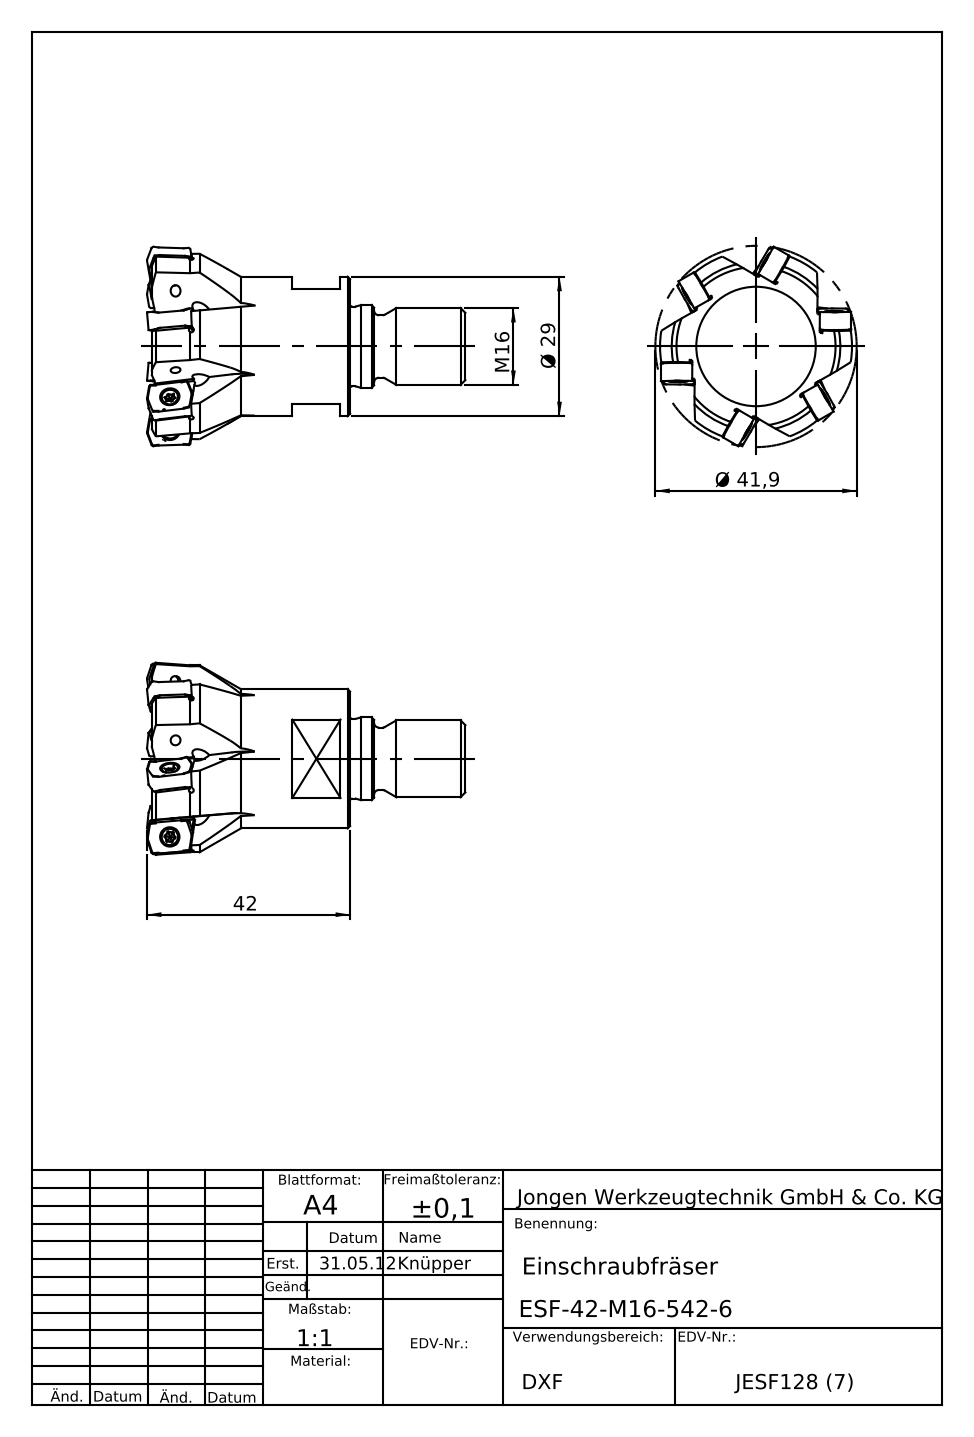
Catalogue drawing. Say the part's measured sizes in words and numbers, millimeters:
The part is named "ESF-42-M16-542-6". Its 3-D file was written by "SolidWorks 2013 (AUTOMOTIVE_DESIGN)". It is 1 solid with 164 faces: 107 planar, 24 cylindrical and 33 other. Overall it measures 66 by 41.99 by 41.99 millimeters. Its volume is 37 457 cubic millimeters and its surface area 9 891 square millimeters. Round holes: 6 of diameter 2.5, 1 of diameter 4. Round bosses or shafts: 1 of diameter 29, 1 of diameter 17.2, 1 of diameter 16.6, 1 of diameter 16, 1 of diameter 13. Partial cylindrical surfaces (rounded edges, fillets, slot ends): 6 of radius 15, 1 of radius 19.45. The main face-to-face distances are 39.8, 24, 63.8, 0.49, 27, 3, 36.8, 37, 13, 10.
